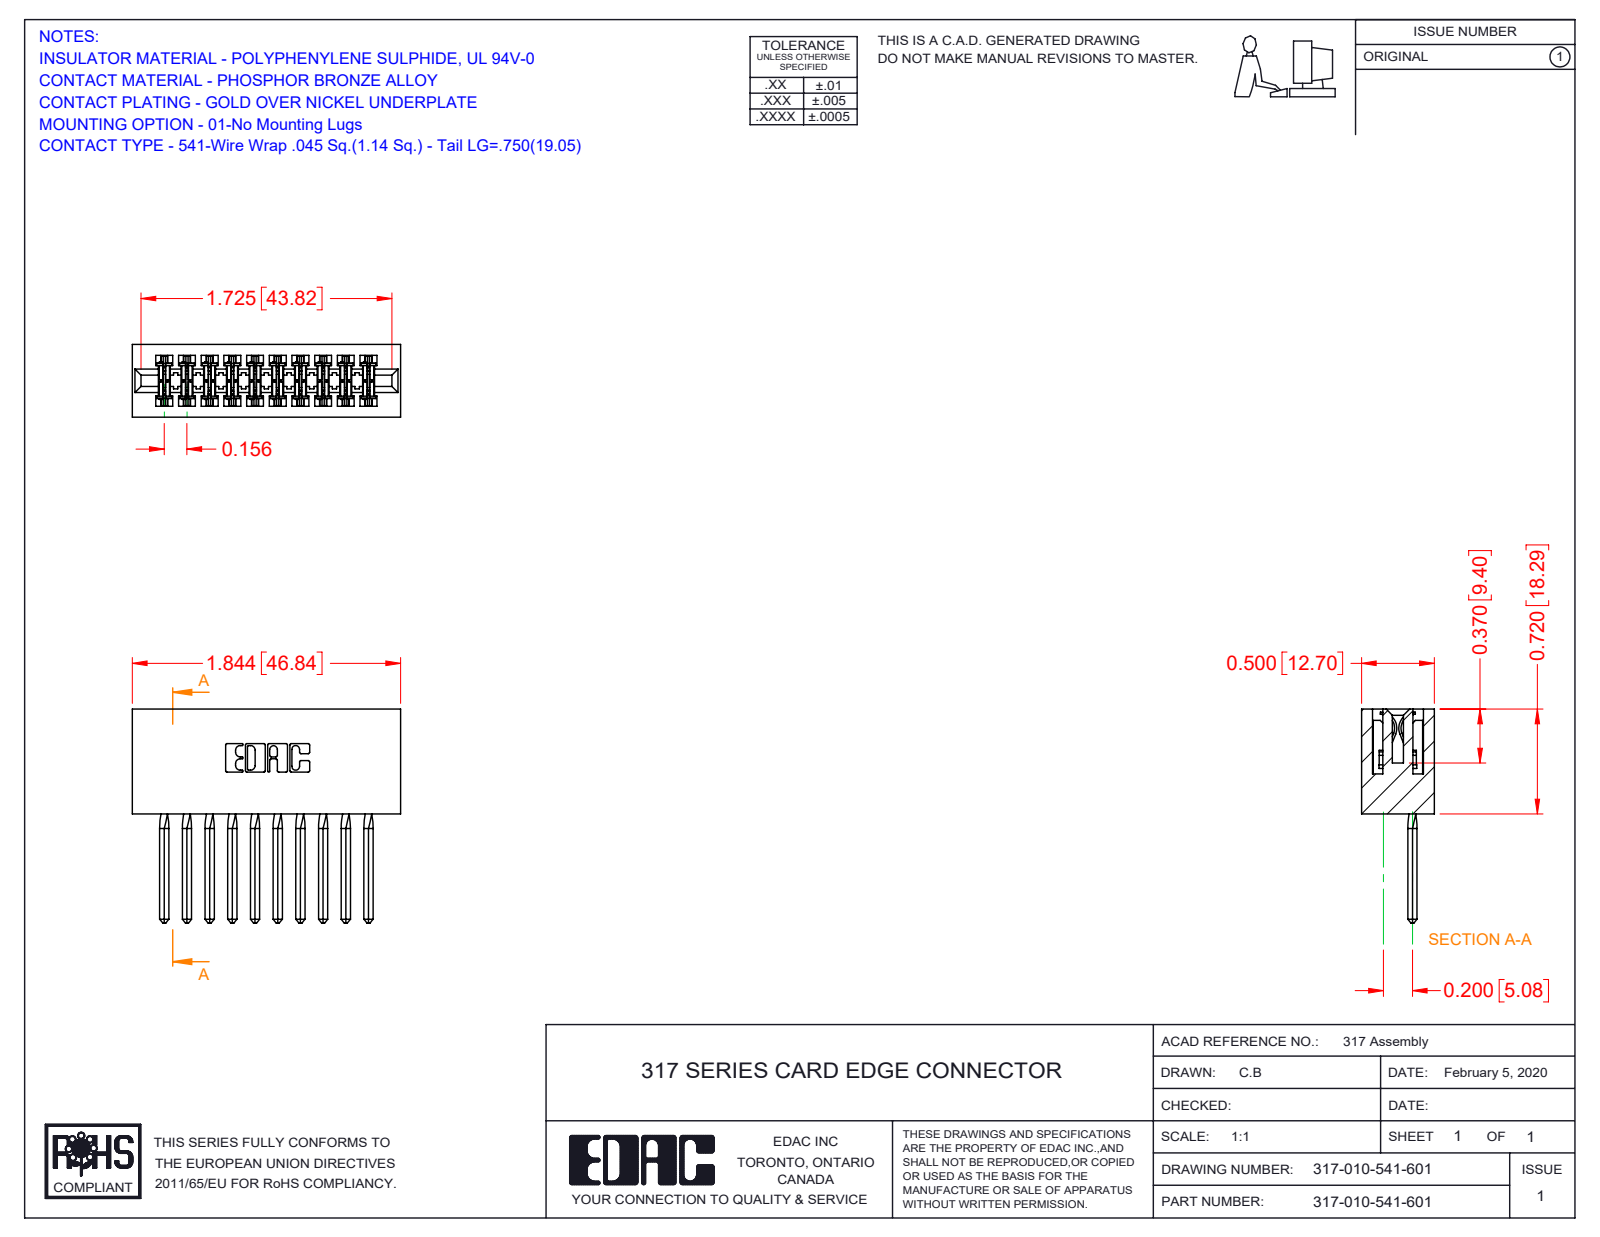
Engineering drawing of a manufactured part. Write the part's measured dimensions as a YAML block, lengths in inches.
part_name: "317-010-541-601; 317-290-002_541; 317 Part_Lugless"
step_written_by: "SolidWorks 2016 (CONFIG_CONTROL_DESIGN)"
units: inches
bodies: {solids: 11, faces: 1610, planar: 1290, cylindrical: 280, other: 40}
overall_size: [1.844, 1.47, 0.5]
volume: 0.508
surface_area: 16.86
partial_cylinders:
  - {radius: 0.01, count: 22}
  - {radius: 0.015, count: 20}
  - {radius: 0.007, count: 6}
  - {radius: 0.031, count: 6}
  - {radius: 0.026, count: 3}
  - {radius: 0.095, count: 2}
  - {radius: 0.1, count: 2}
  - {radius: 0.11, count: 2}
face_to_face_distances: [0.5, 0.075, 0.425, 0.11, 0.065, 0.22, 0.156, 0.331, 0.624, 0.35]
